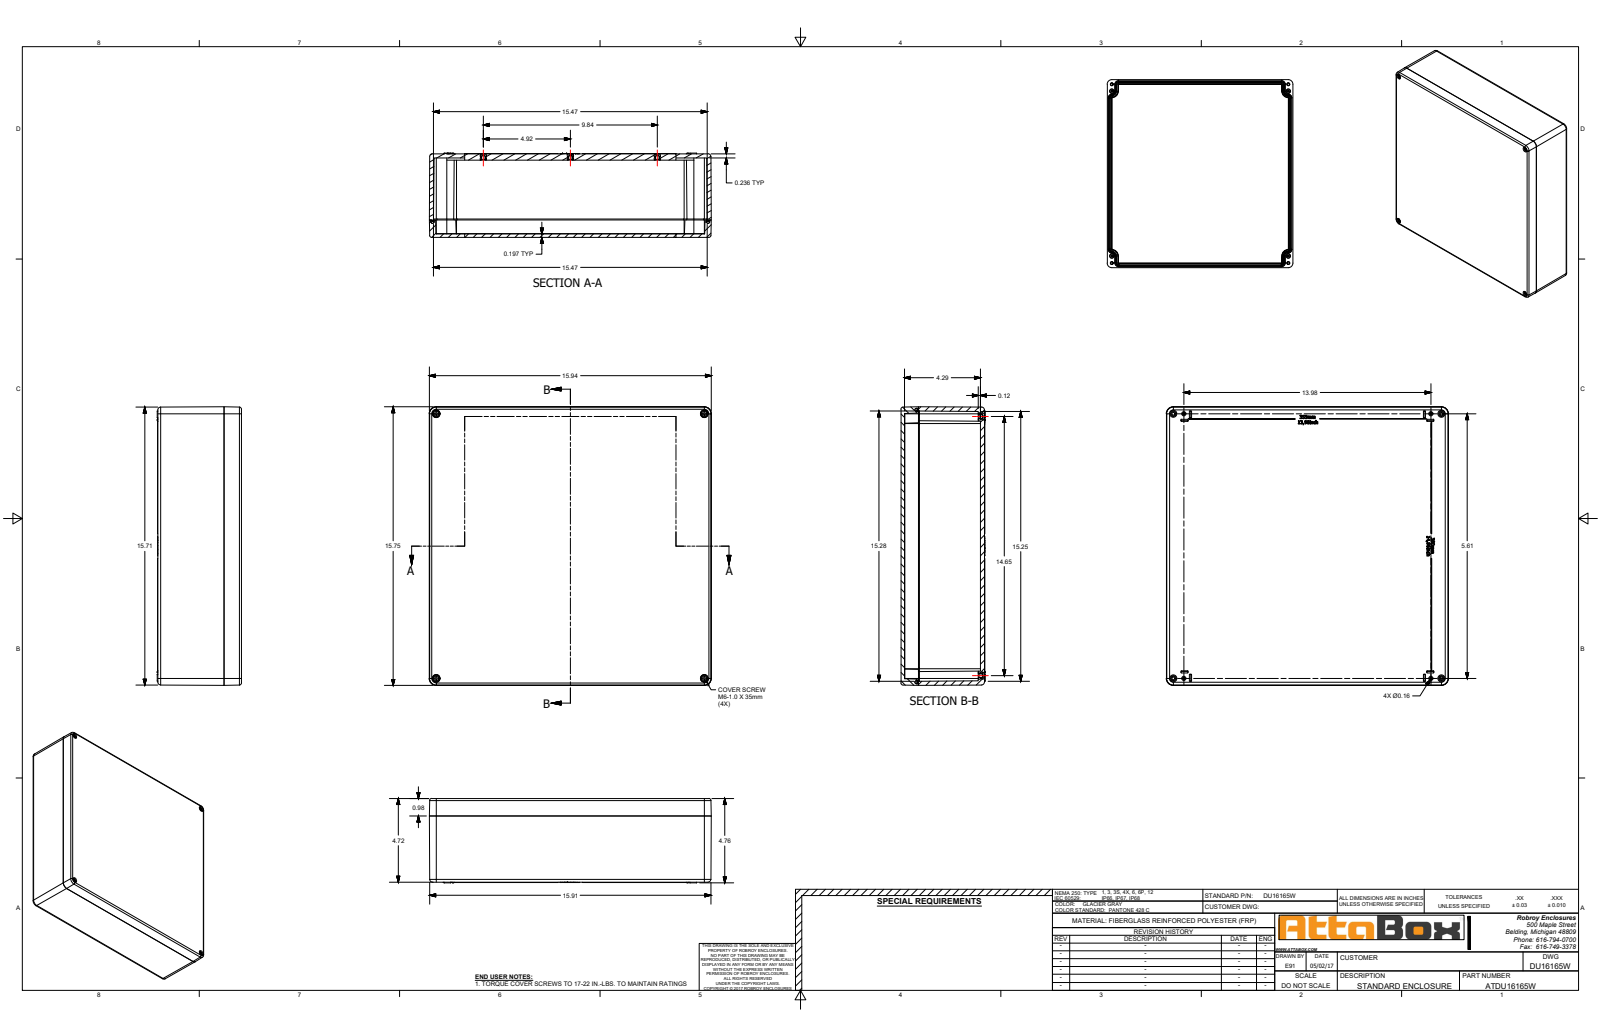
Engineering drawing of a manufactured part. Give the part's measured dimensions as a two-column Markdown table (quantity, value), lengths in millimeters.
| quantity | value |
| --- | --- |
| part name | DU16165W |
| STEP written by | SolidWorks 2018 (AUTOMOTIVE_DESIGN) |
| units | millimeters |
| bodies | 17 solids, 1345 faces (645 planar, 170 cylindrical, 530 other) |
| overall size | 405 × 400 × 121 |
| volume | 3 055 000 mm³ |
| surface area | 1 085 000 mm² |
| round holes (diameter × count) | 4.9 × 10, 6 × 6, 5.4 × 4, 7 × 4 |
| round bosses / shafts (diameter × count) | 7.4 × 10, 9.5 × 4, 8 × 4, 6 × 4, 5.2 × 4 |
| partial cylindrical surfaces (radius × count) | 0.5 × 32, 2.3 × 16, 4.2 × 8, 6.2 × 8, 8.7 × 8, 10.7 × 8, 0.4 × 6, 3 × 4 |
| main face-to-face distances | 120, 115, 5, 114, 6, 109, 25, 20, 95, 89 |
| hole center spacings | 67.6, 125, 192.5, 317.5, 382, 392.4, 422.4, 492.1 |
